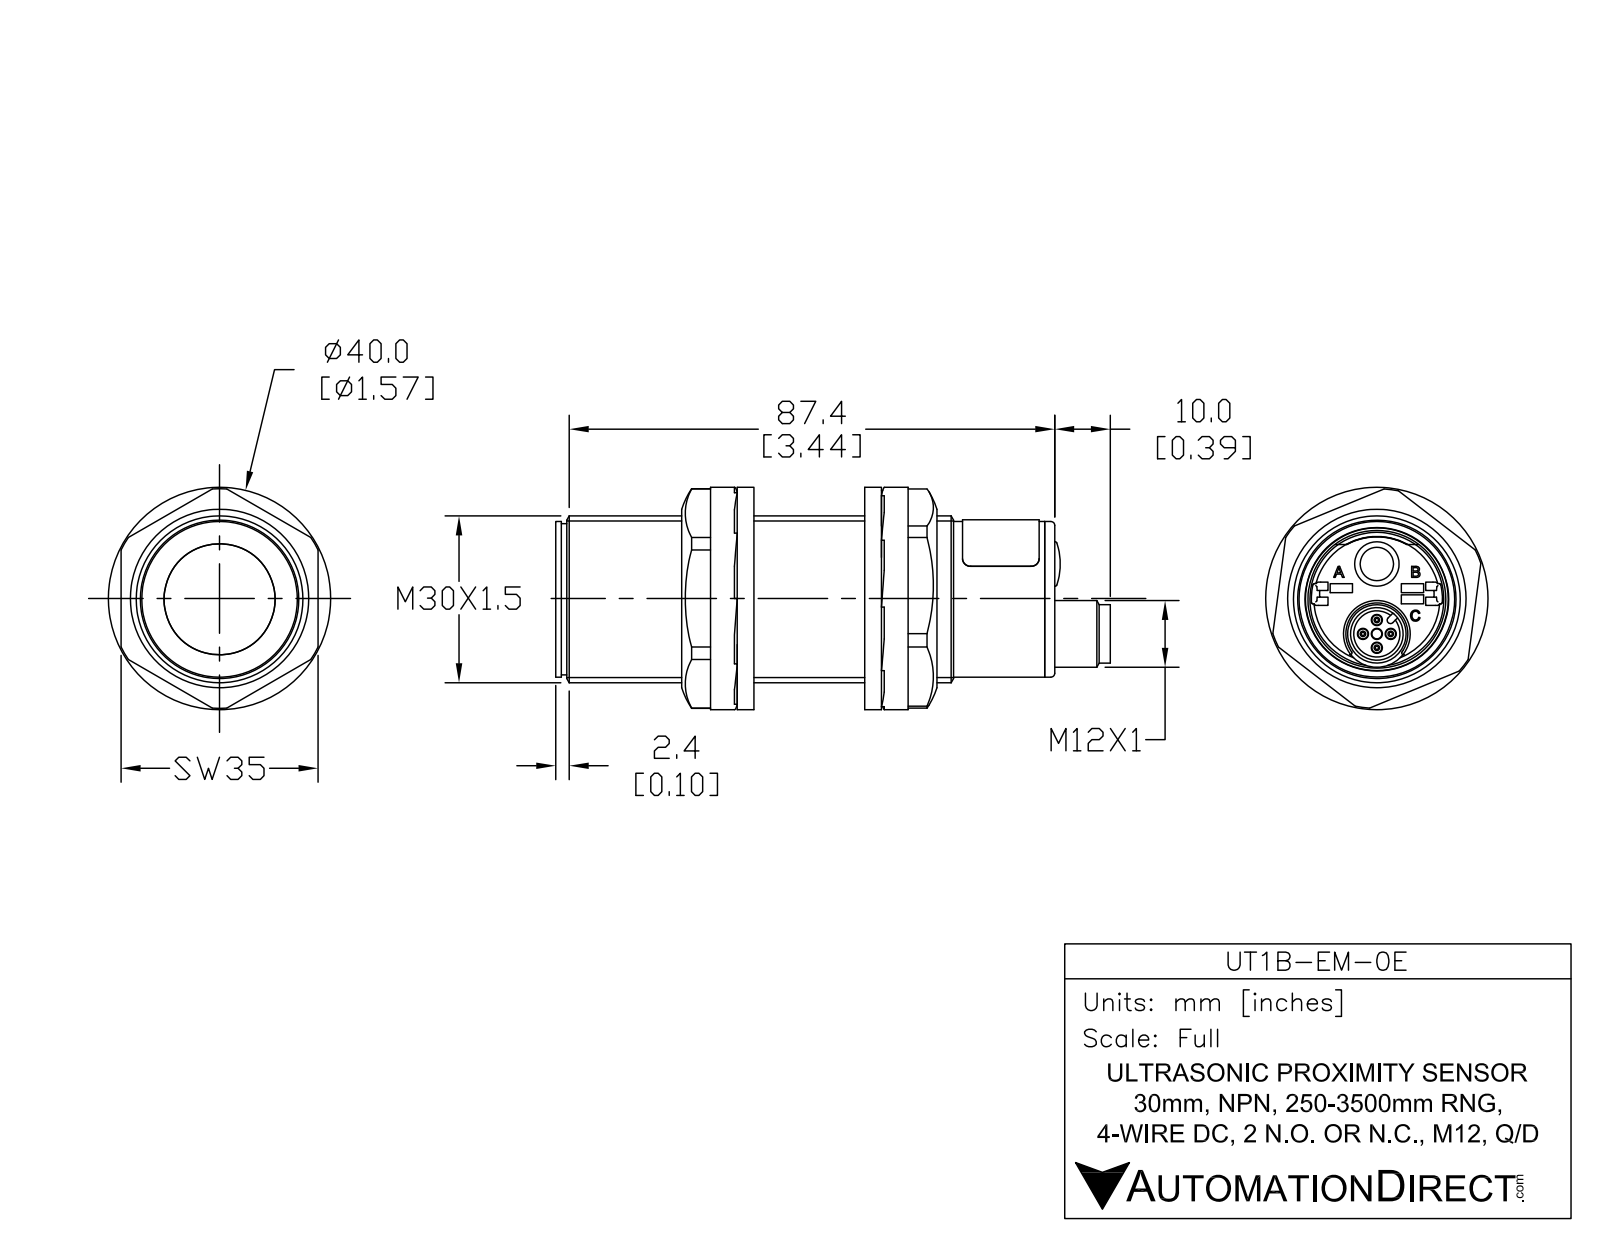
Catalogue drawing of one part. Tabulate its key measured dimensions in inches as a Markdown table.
| quantity | value |
| --- | --- |
| part name | UT1B-EM-0E |
| STEP written by | SolidWorks 2017 (AUTOMOTIVE_DESIGN) |
| units | inches |
| bodies | 5 solids, 107 faces (30 planar, 45 cylindrical, 32 other) |
| overall size | 3.89 × 1.181 × 1.181 |
| volume | 3.754 in³ |
| surface area | 20.71 in² |
| round holes (diameter × count) | 0.071 × 4, 0.315 × 1, 0.327 × 1, 0.372 × 1, 0.925 × 1 |
| round bosses / shafts (diameter × count) | 0.039 × 4, 1.181 × 1, 1.102 × 1, 1.071 × 1, 0.472 × 1, 0.413 × 1, 0.364 × 1 |
| partial cylindrical surfaces (radius × count) | 0.012 × 2, 0.024 × 1 |
| main face-to-face distances | 3.386, 3.457, 0.039, 3.425, 0.071, 3.496, 0.039, 0.059, 3.425, 3.496 |
| hole center spacings | 0.098, 0.139, 0.197, 0.264, 0.505, 0.146, 0.245, 0.25 |
